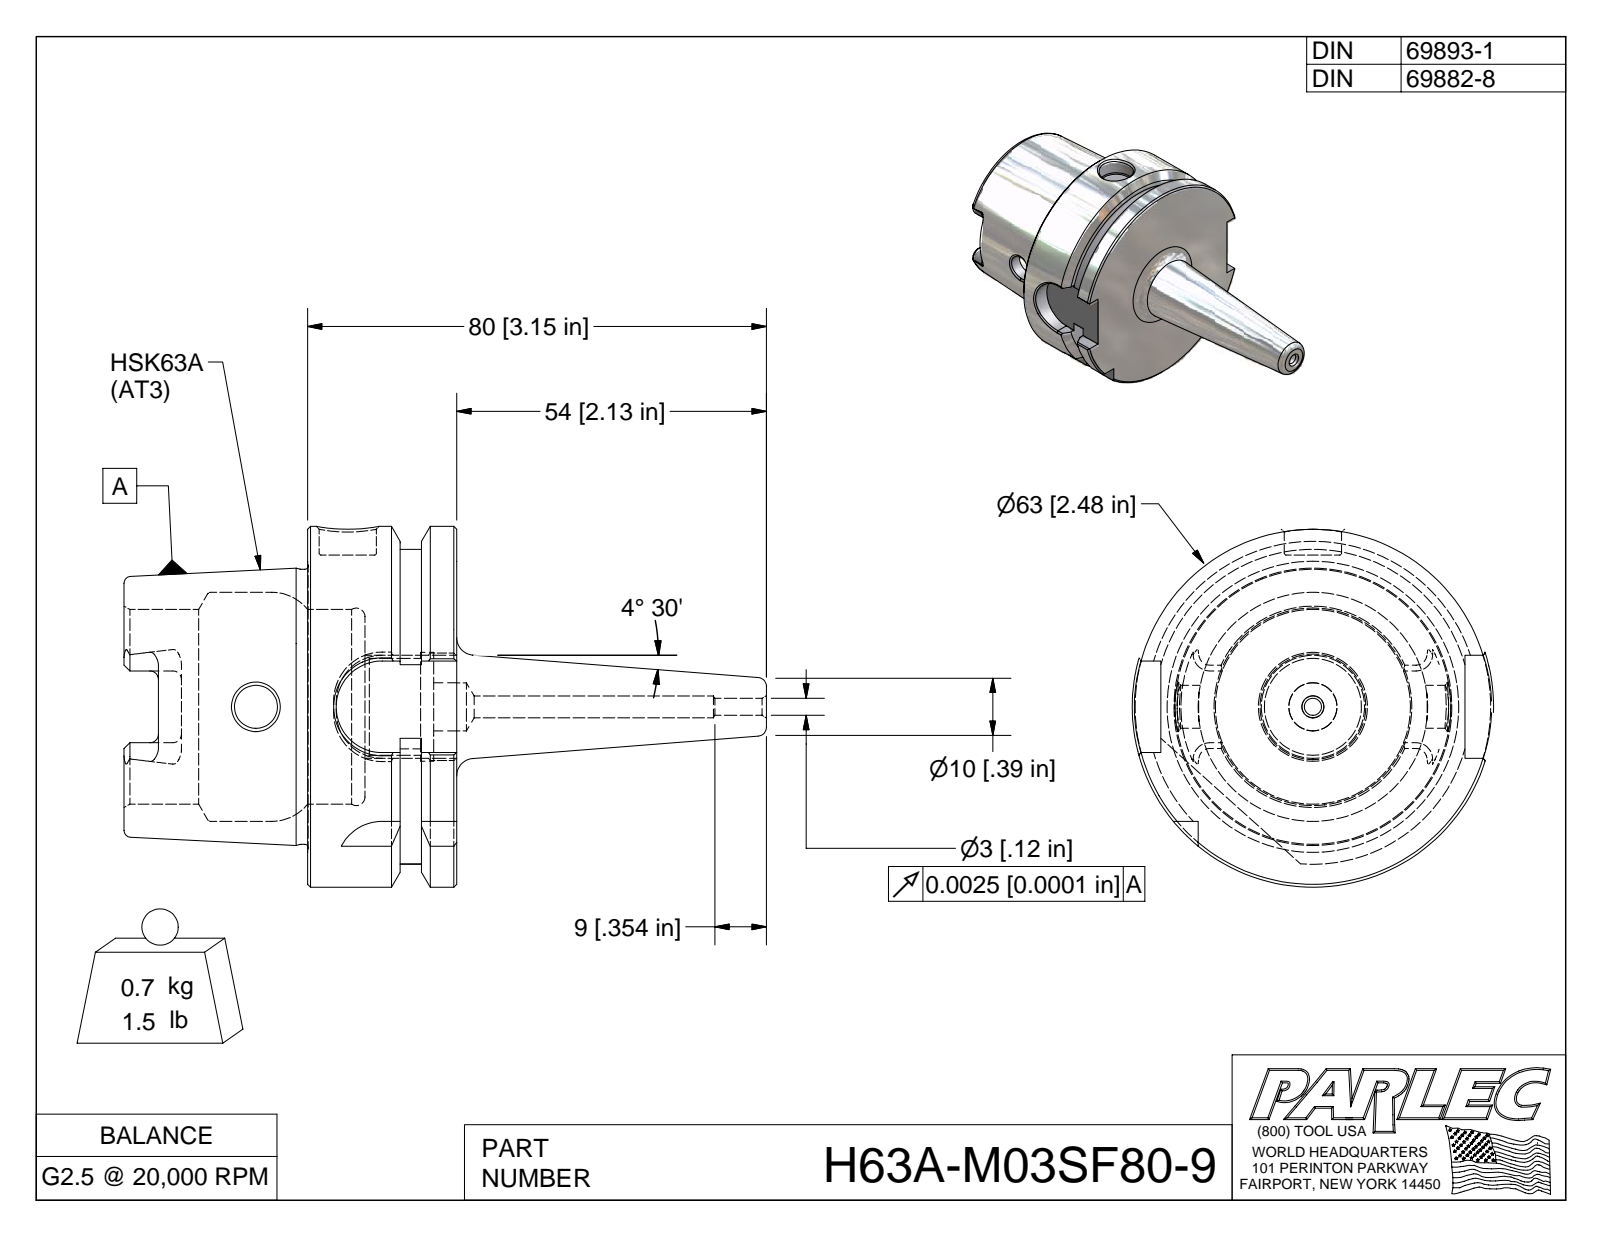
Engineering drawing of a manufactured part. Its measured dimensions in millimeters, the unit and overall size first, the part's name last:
Units: millimetres
Overall size (bounding box): 112 × 63 × 63
Round holes (diameter × count): ⌀3 ×1, ⌀7.5 ×1, ⌀8.4 ×1, ⌀10 ×1, ⌀16.9 ×1, ⌀19 ×1, ⌀34 ×1, ⌀40 ×1
Round bosses / shafts (diameter × count): ⌀63 ×1, ⌀48 ×1
Partial cylindrical surfaces — rounded edges, fillets, slot ends (radius × count): R1.5 ×6, R2.9 ×4, R8 ×4, R27.5 ×1
Main face-to-face distances: 26, 6.1, 9.9, 10, 16, 32, 58, 42, 48.1, 16.1
Volume: 89 340 mm³ · Surface area: 25 390 mm²
Bodies: 1 solid, 137 faces (48 planar, 33 cylindrical, 56 other)
Part name (STEP PRODUCT): H63A-M03SF80-9; H63A-M03SF80-9-1
STEP written by: Autodesk Inventor 2009 (AUTOMOTIVE_DESIGN)
